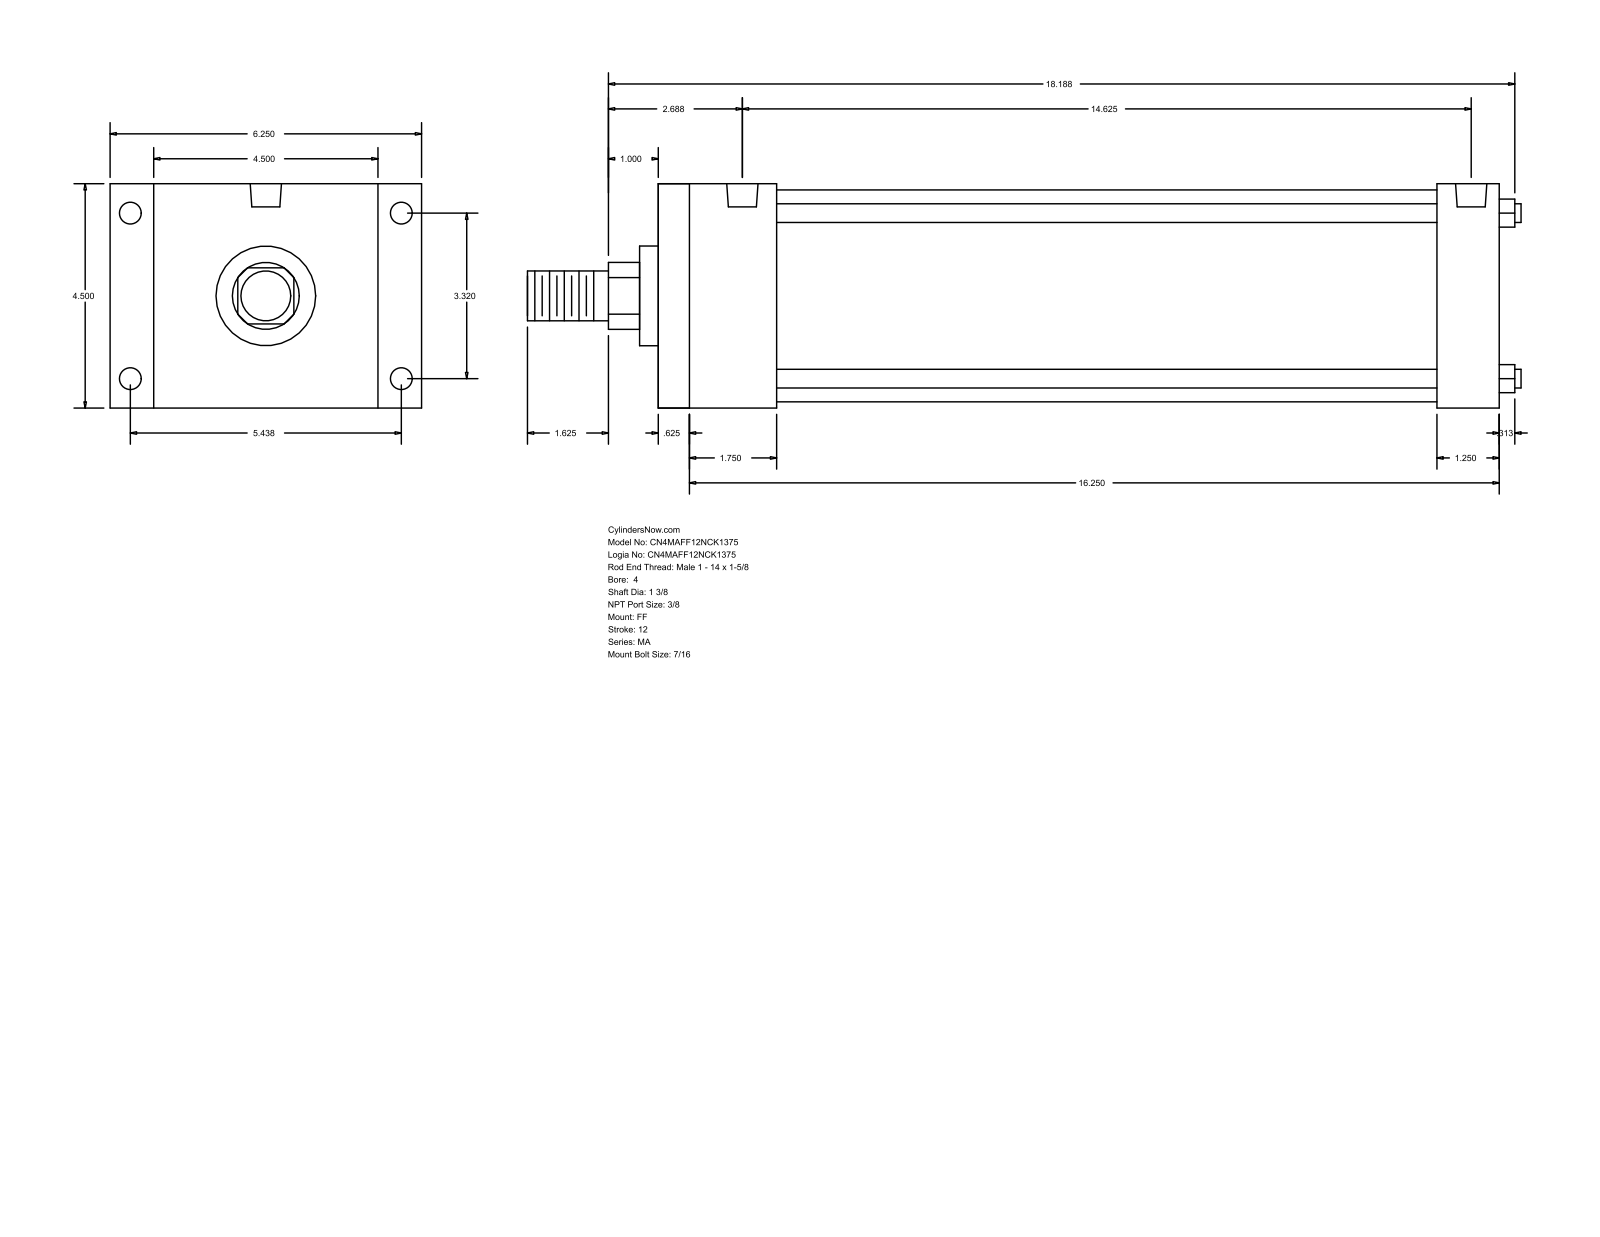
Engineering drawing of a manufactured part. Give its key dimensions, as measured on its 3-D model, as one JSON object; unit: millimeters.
{"part_name": "MA_FF__0400_1.375", "step_written_by": "GSSL Pune (CONFIG_CONTROL_DESIGN)", "units": "millimeters", "bodies": {"solids": 0, "faces": 92, "planar": 64, "cylindrical": 28, "other": 0}, "overall_size": [506.41, 158.75, 114.3], "round_holes": [[11.11, 8], [15.93, 2]], "round_bosses_or_shafts": [[9.53, 4], [107.95, 1], [50.8, 1], [34.92, 1], [25.4, 1]], "partial_cylinders_radius": [[17.06, 1]], "face_to_face_distances": [114.3, 428.62, 15.87, 412.75, 22.23, 136.53, 396.87, 381, 31.75, 60.32], "hole_center_spacings": [84.32, 138.12, 161.82, 361.95, 4.76, 4.77, 366.71, 366.72]}
